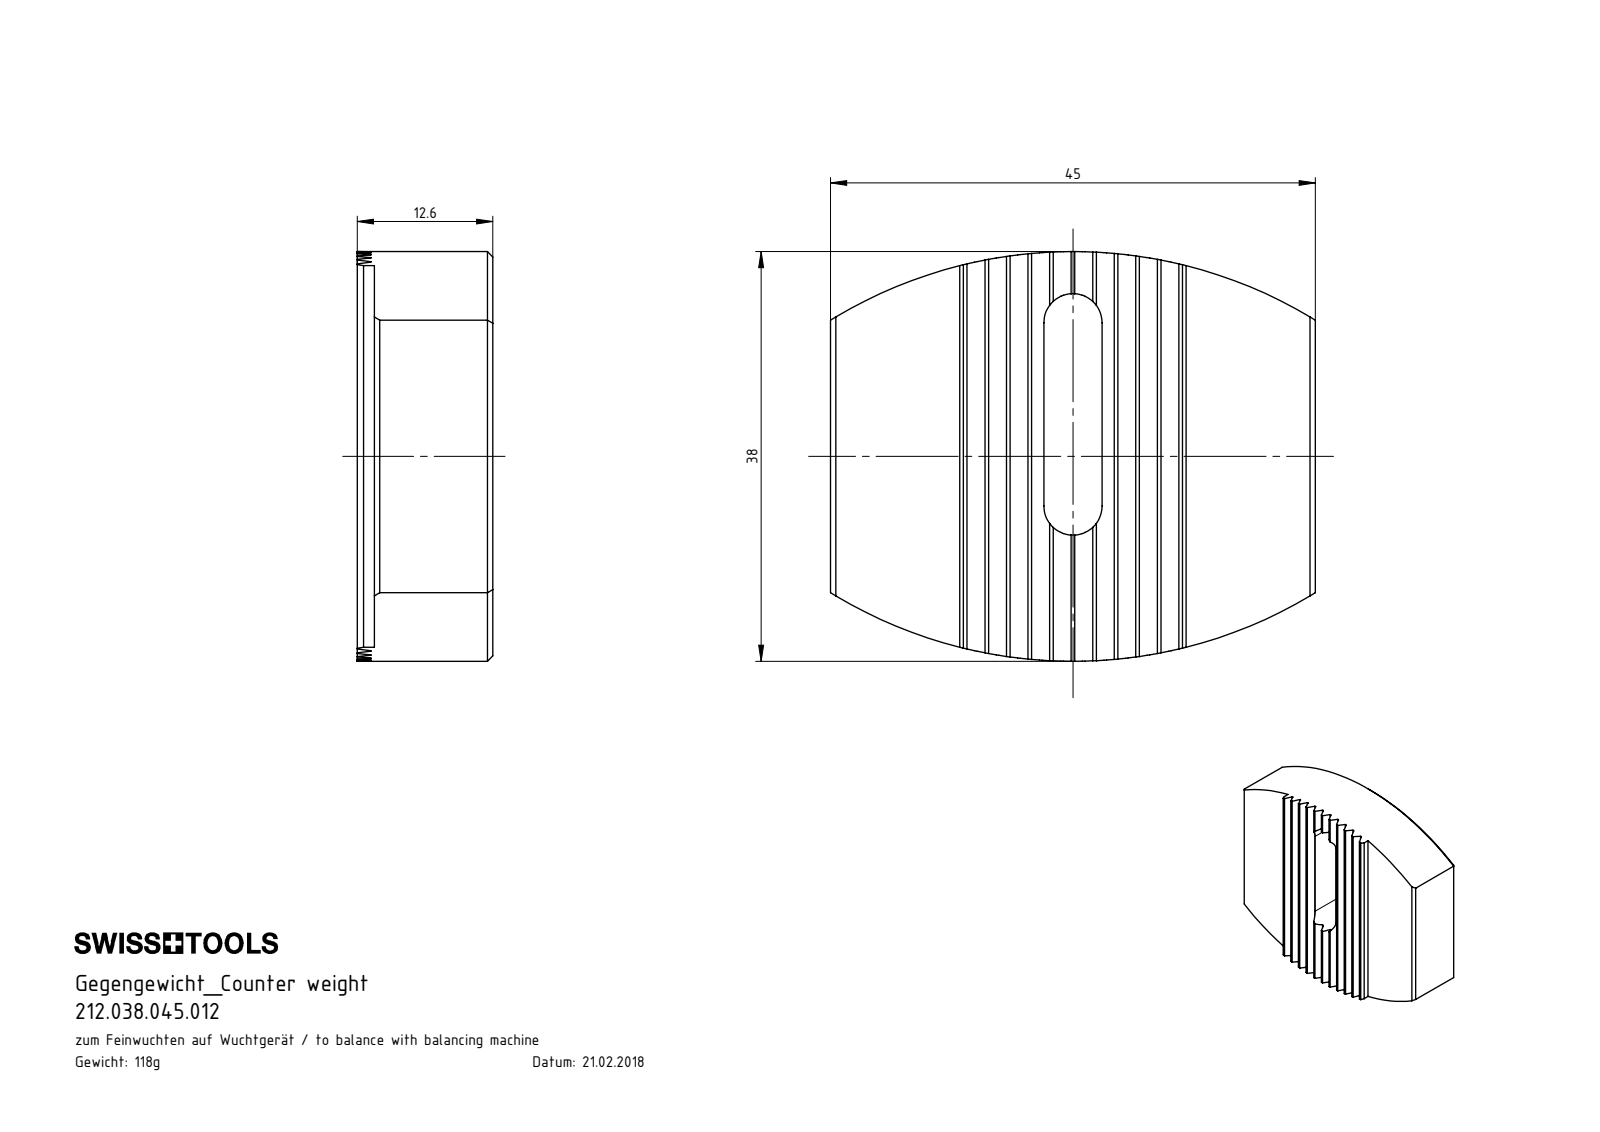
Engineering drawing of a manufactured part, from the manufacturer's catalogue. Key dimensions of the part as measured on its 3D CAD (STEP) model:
Part name (STEP PRODUCT): 212.038.045.012
STEP written by: SolidWorks 2017 (CONFIG_CONTROL_DESIGN)
Units: millimetres
Bodies: 1 solid, 90 faces (56 planar, 32 cylindrical, 2 other)
Overall size (bounding box): 45 × 38 × 12.58
Volume: 15 083 mm³ · Surface area: 5 672 mm²
Partial cylindrical surfaces — rounded edges, fillets, slot ends (radius × count): R0.14 ×10, R2.7 ×2, R5.75 ×2, R43 ×2
Main face-to-face distances: 11, 1.73, 5.2, 8.66, 3.46, 10.39, 6.93, 12.12, 45, 5.19
